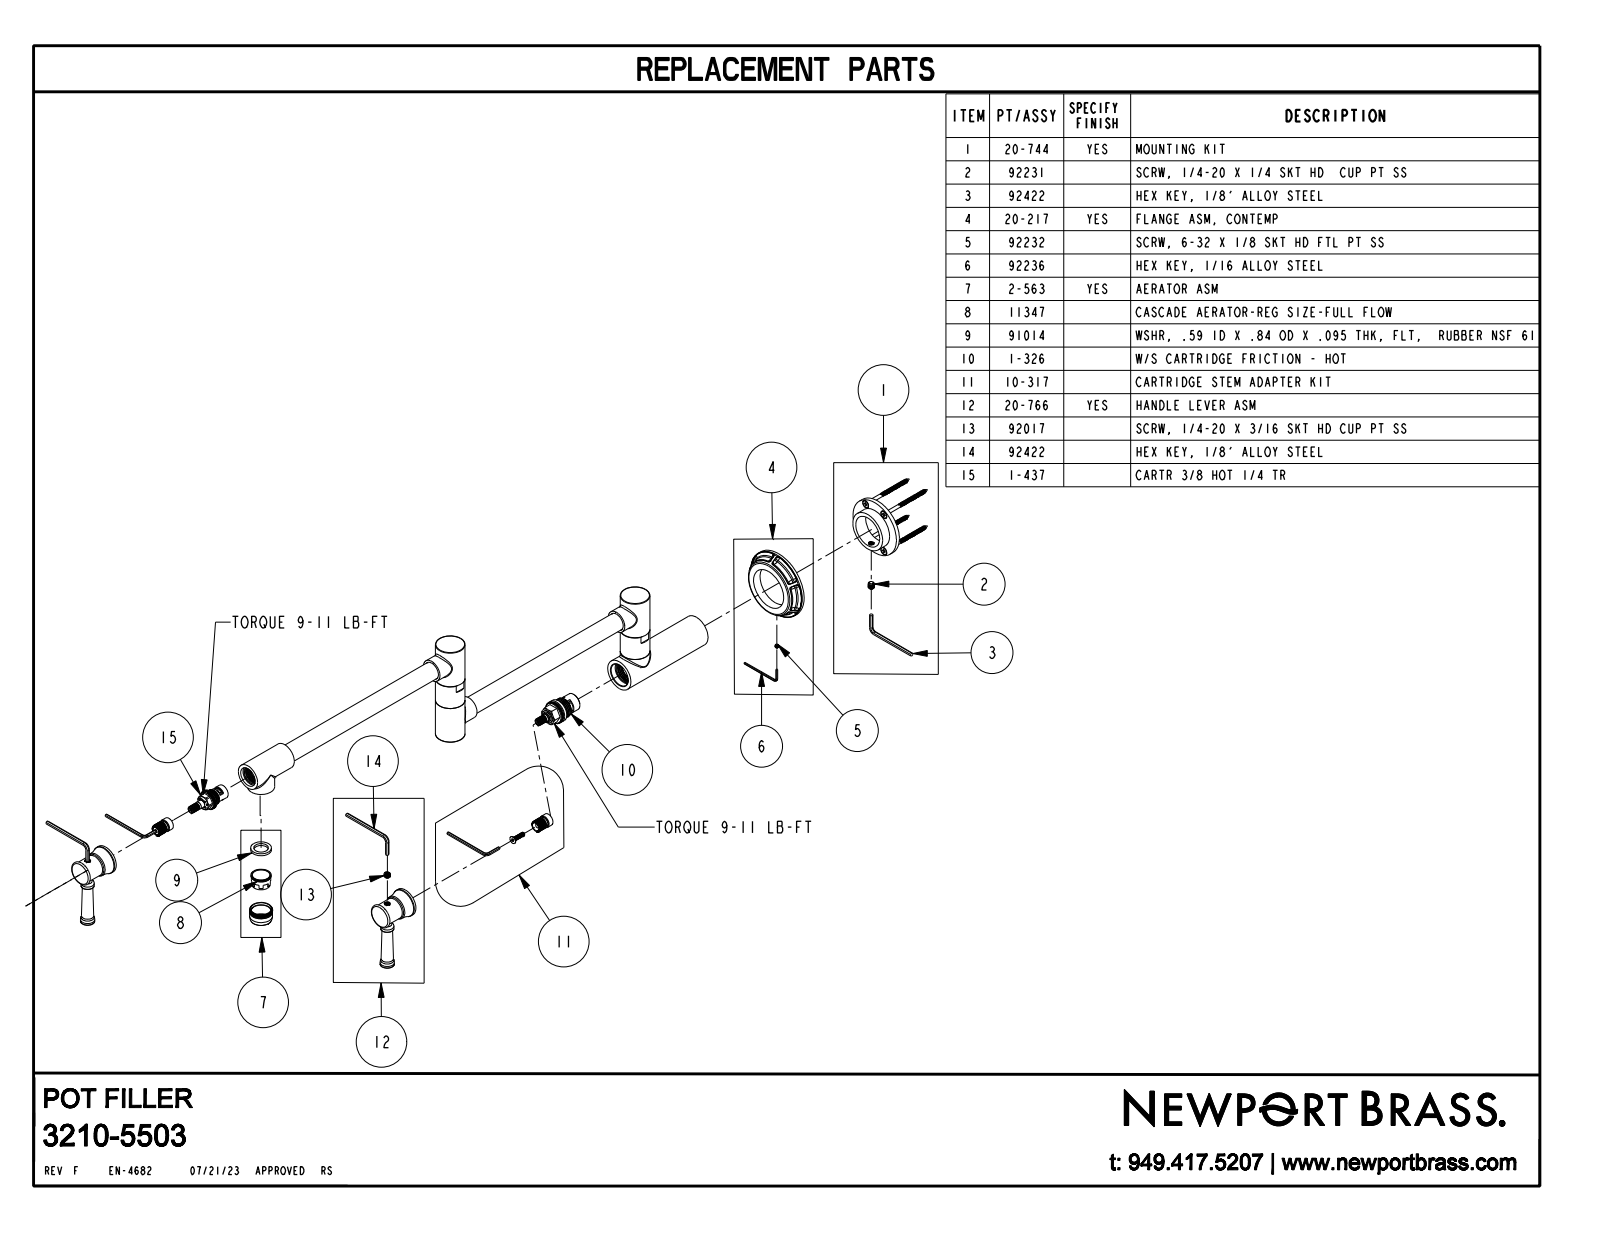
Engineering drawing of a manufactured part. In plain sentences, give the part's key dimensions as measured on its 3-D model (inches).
The part is named "3210-5503". Its 3-D file was written by "CREO PARAMETRIC BY PTC INC, 2018400 (CONFIG_CONTROL_DESIGN)". It is 1 solid with 358 faces: 46 planar, 66 cylindrical and 246 other. Overall it measures 27.139 by 8.946 by 2.92 inches. Its volume is 31.2 cubic inches and its surface area 138.9 square inches. Round holes: 2 of diameter 0.375. Round bosses or shafts: 4 of diameter 0.94, 2 of diameter 1.2, 2 of diameter 1.19, 2 of diameter 1.1, 2 of diameter 0.9, 2 of diameter 0.775, 2 of diameter 0.75, 2 of diameter 0.636. Partial cylindrical surfaces (rounded edges, fillets, slot ends): 1 of radius 0.472, 1 of radius 1.232. The main face-to-face distances are 0.57, 2.86, 21.248, 1.47, 1.576, 4.437, 1.676, 0.02, 1.696, 4.41. The hole center spacings are 21.248.
